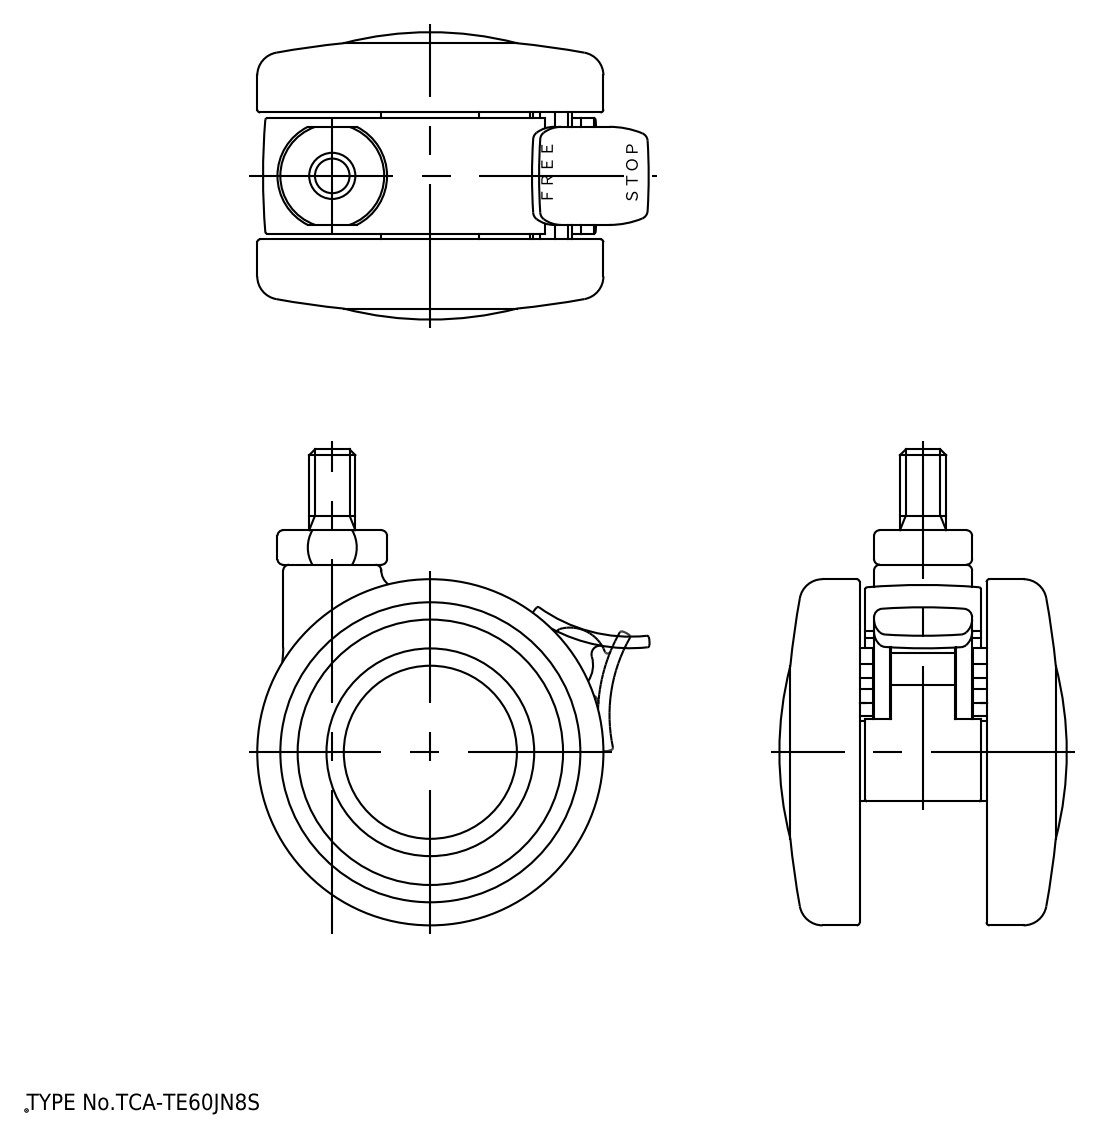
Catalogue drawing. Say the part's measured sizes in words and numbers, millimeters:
The part is named "TCA-TE60J_Wheel; TCA-TE60JN8_Shaft; TCA-TE60JS_Body; TCA-TE60JS_Stopper". Its 3-D file was written by "spGate 18.9.1 (****-****-****-****) (AUTOMOTIVE_DESIGN)". It is 5 solids with 260 faces: 67 planar, 114 cylindrical and 79 other. Overall it measures 82.5 by 68.87 by 49.14 millimeters. Its volume is 84 903 cubic millimeters and its surface area 33 728 square millimeters. Round holes: 1 of diameter 3.5, 1 of diameter 8, 1 of diameter 9.3, 1 of diameter 10.7, 1 of diameter 20, 1 of diameter 30.2, 1 of diameter 45. Round bosses or shafts: 1 of diameter 60, 1 of diameter 36, 1 of diameter 29.9, 1 of diameter 18, 1 of diameter 17, 1 of diameter 10.5, 1 of diameter 8, 1 of diameter 6.5. Partial cylindrical surfaces (rounded edges, fillets, slot ends): 6 of radius 0.3, 5 of radius 1, 5 of radius 1.5, 5 of radius 2, 2 of radius 15, 2 of radius 26.5, 2 of radius 29, 2 of radius 99.73. The main face-to-face distances are 5, 11, 2, 26, 7, 30.5, 19, 24, 21, 28.5. The hole center spacings are 27.5.
